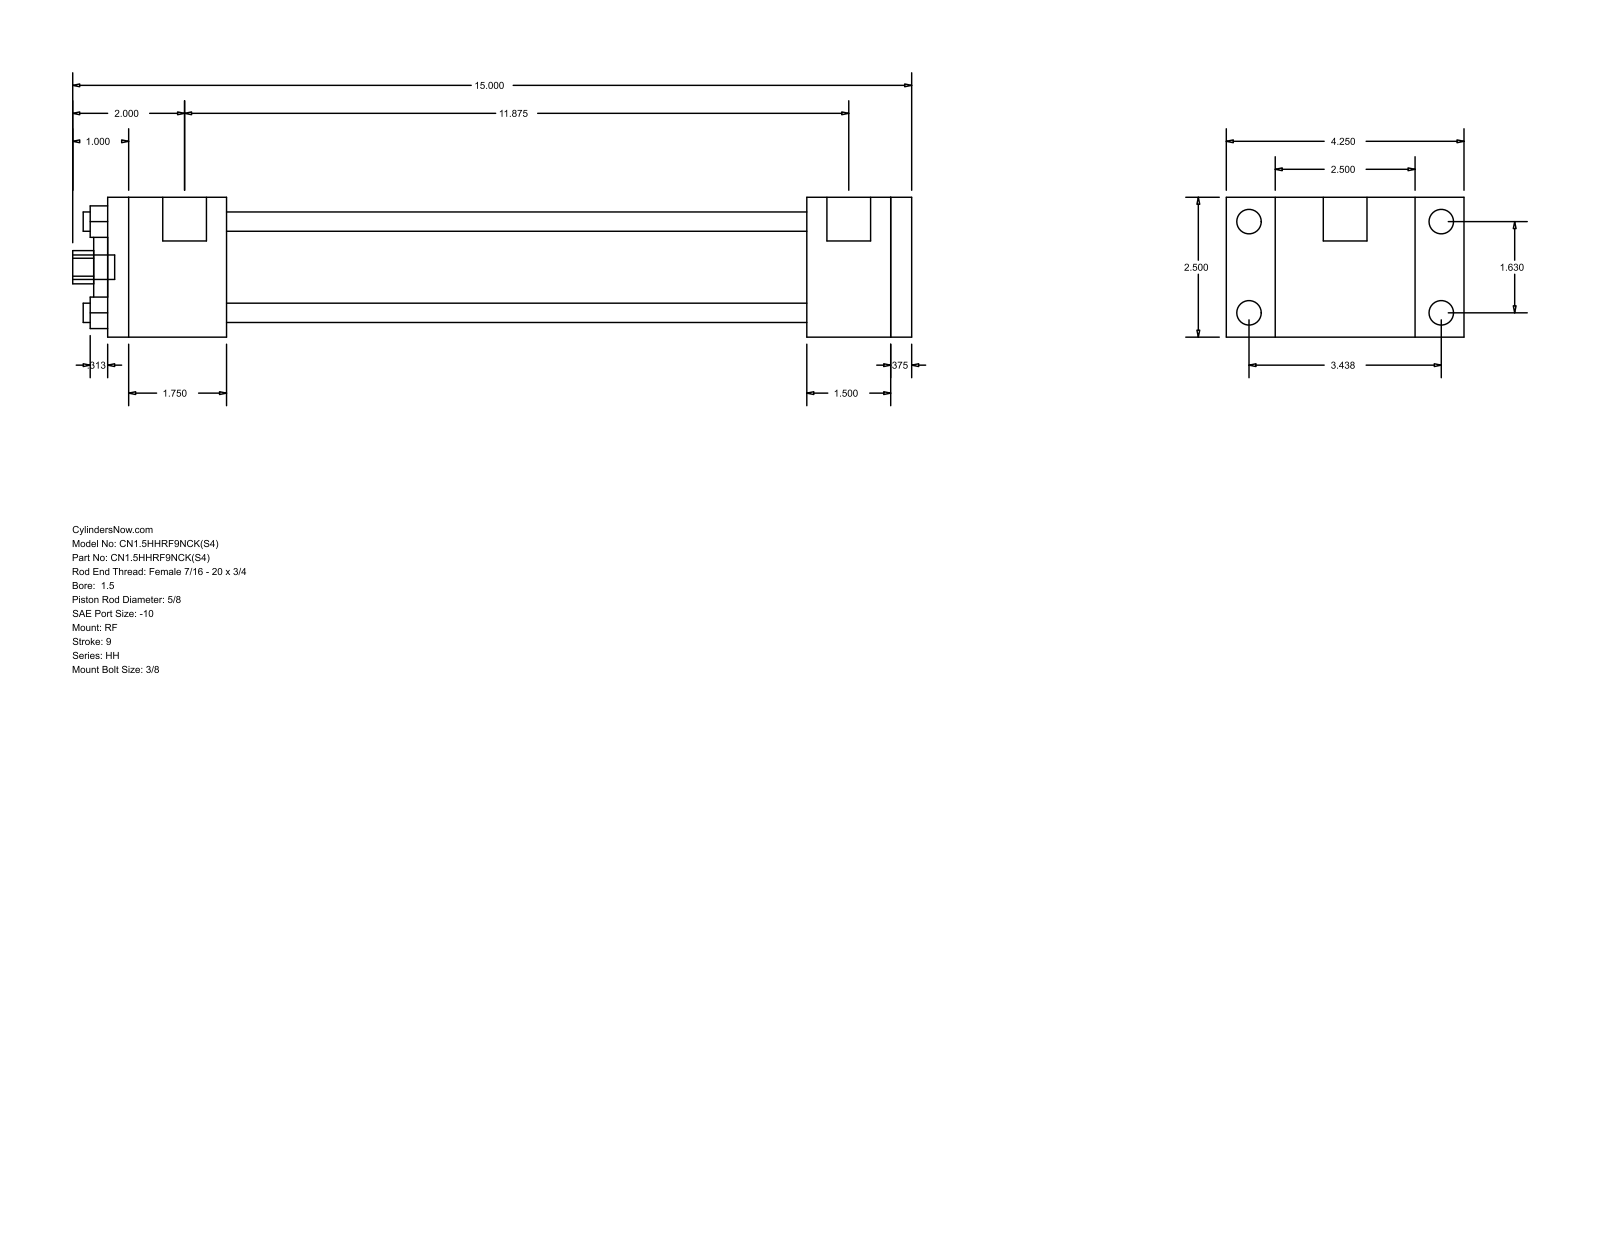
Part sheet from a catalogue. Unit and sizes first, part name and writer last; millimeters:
Units: millimetres
Overall size (bounding box): 381 × 107.95 × 63.5
Round holes (diameter × count): ⌀8.76 ×4, ⌀15.88 ×1, ⌀28.57 ×1, ⌀44.45 ×1
Round bosses / shafts (diameter × count): ⌀11.13 ×4, ⌀5.56 ×4, ⌀19.84 ×2, ⌀11.11 ×1
Partial cylindrical surfaces — rounded edges, fillets, slot ends (radius × count): R7.54 ×1
Main face-to-face distances: 63.5, 365.12, 9.52, 38.1, 355.6, 53.97, 317.5, 263.53, 301.63, 311.15
Hole centre spacings: 29.27, 41.4, 58.55
Bodies: 0 solids, 92 faces (64 planar, 28 cylindrical, 0 other)
Part name (STEP PRODUCT): HH_RF__0150_0.625
STEP written by: GSSL Pune (CONFIG_CONTROL_DESIGN)
